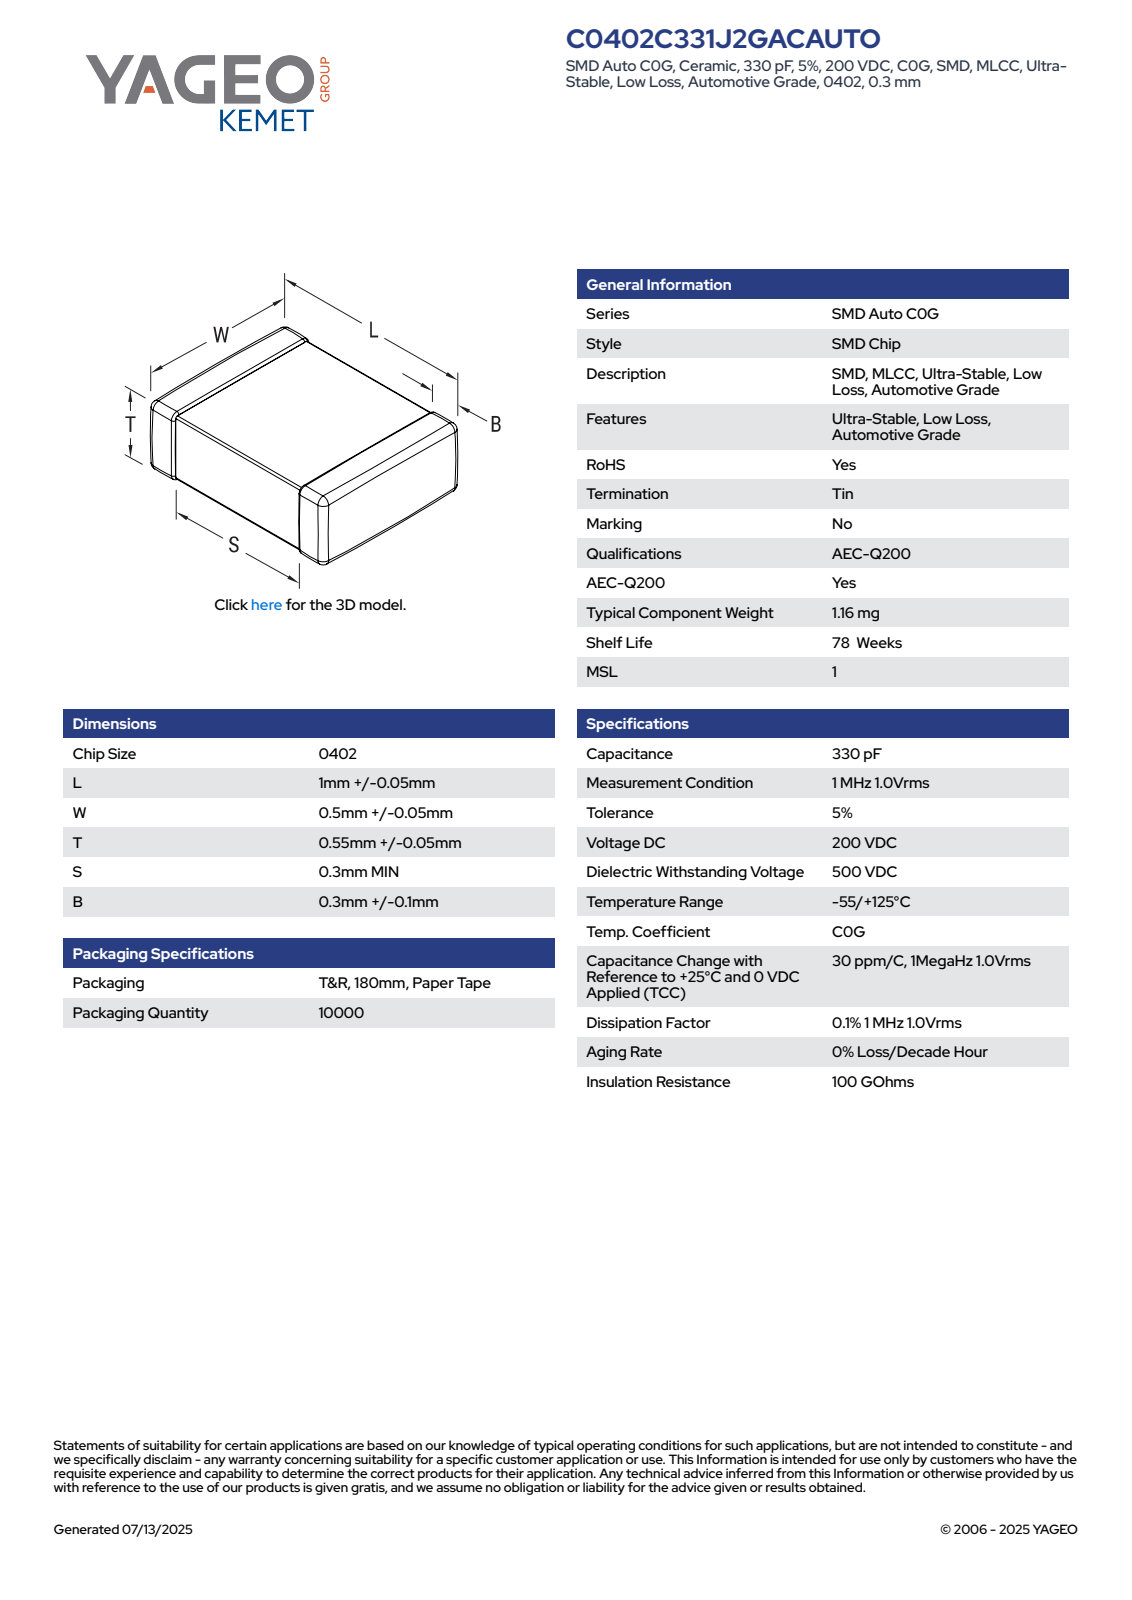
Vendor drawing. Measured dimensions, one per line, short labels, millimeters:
name: CCS_CCSTD_0402_L1.05W0.55T0.6B0.3
written by: SolidWorks 2014 (AUTOMOTIVE_DESIGN)
unit: mm
bodies: 4 solids, 125 faces (71 planar, 38 cylindrical, 16 other)
size: 1.05 × 0.6 × 0.55
volume: 0.335 mm³; area: 3 mm²
face distances: 0.54, 0.59, 0.55, 1.05, 0.6, 0.53, 0.58, 0.49, 0.56, 0.57
